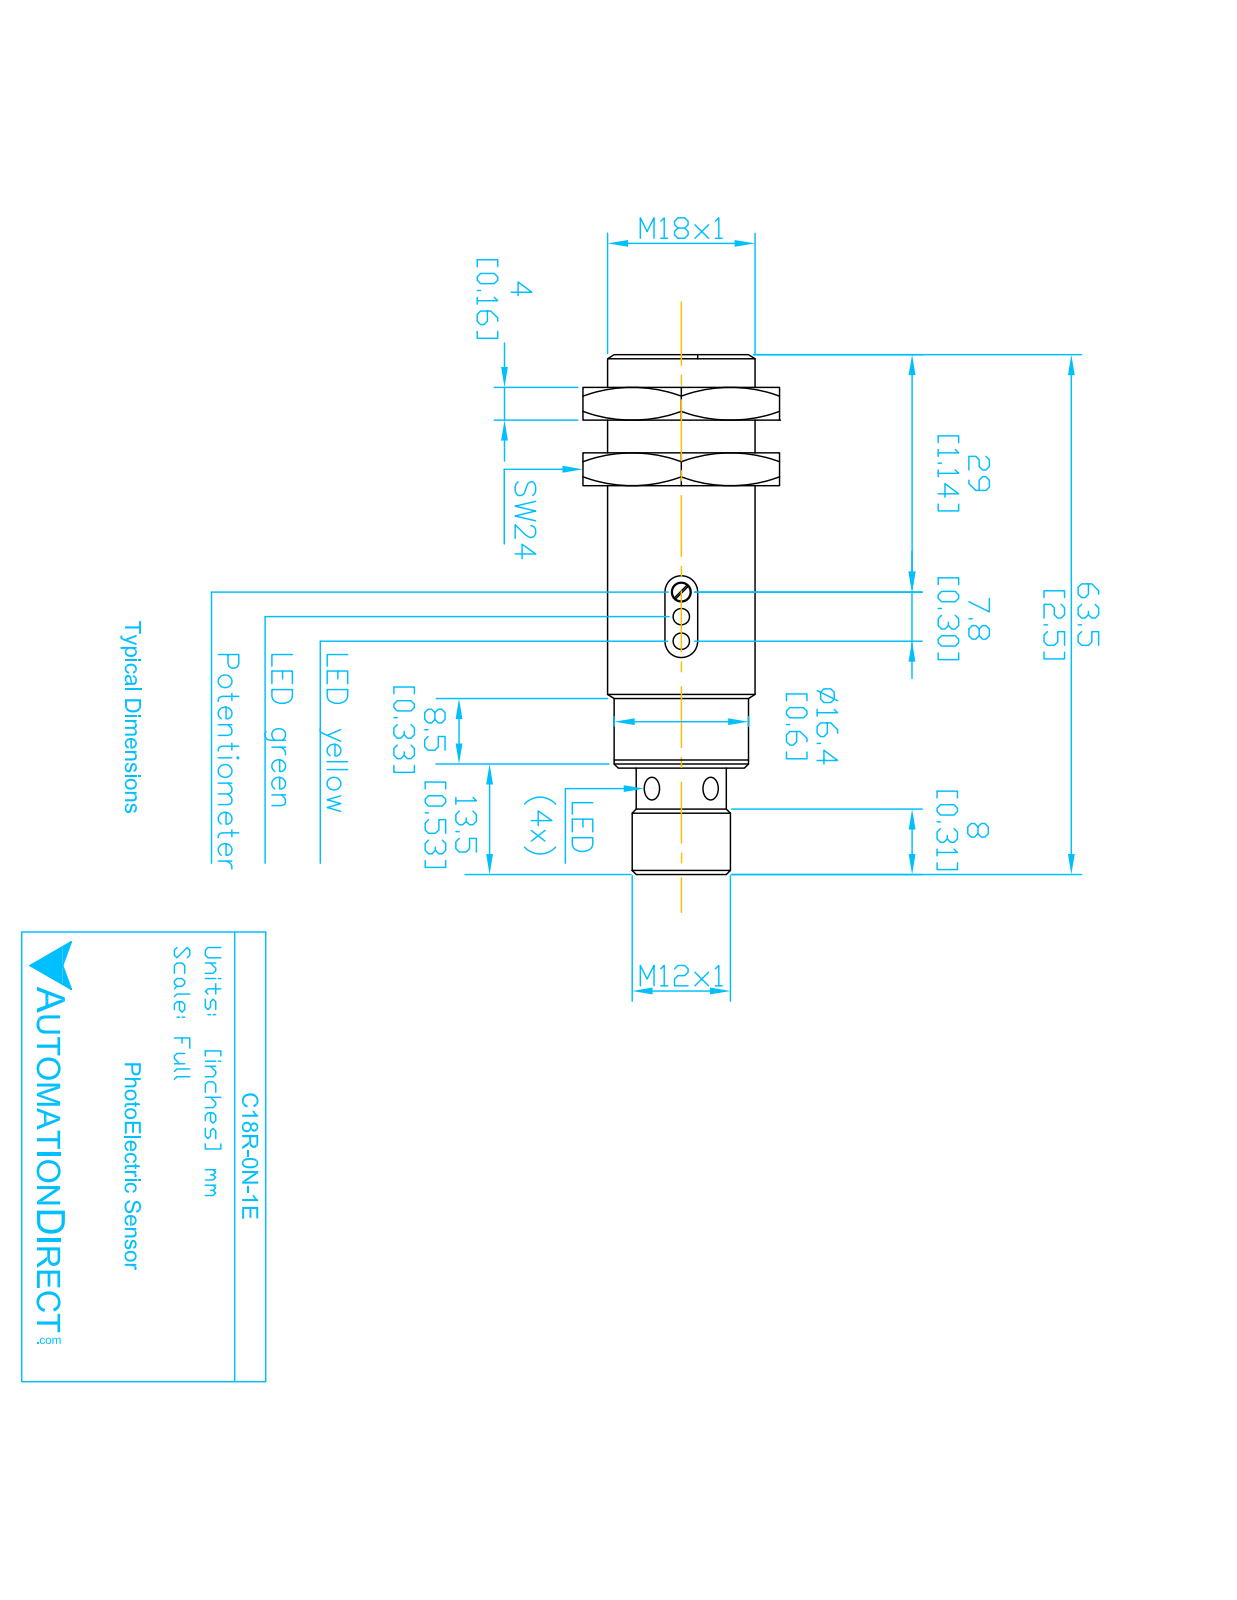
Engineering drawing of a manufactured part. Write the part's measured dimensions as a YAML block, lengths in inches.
part_name: "C18R-0N-1E"
step_written_by: "SolidWorks 2017 (AUTOMOTIVE_DESIGN)"
units: inches
bodies: {solids: 6, faces: 74, planar: 20, cylindrical: 36, other: 18}
overall_size: [2.5, 0.709, 0.709]
volume: 0.807
surface_area: 7.011
round_holes:
  - {diameter: 0.118, count: 3}
  - {diameter: 0.335, count: 1}
round_bosses_or_shafts:
  - {diameter: 0.04, count: 4}
  - {diameter: 0.709, count: 1}
  - {diameter: 0.646, count: 1}
  - {diameter: 0.459, count: 1}
  - {diameter: 0.415, count: 1}
partial_cylinders:
  - {radius: 0.02, count: 2}
  - {radius: 0.089, count: 2}
  - {radius: 0.185, count: 1}
  - {radius: 0.2, count: 1}
face_to_face_distances: [2.157, 2.047, 0.11, 0.039, 2.008, 0.15, 2.5, 0.492, 0.453, 0.343]
hole_center_spacings: [1.004]
